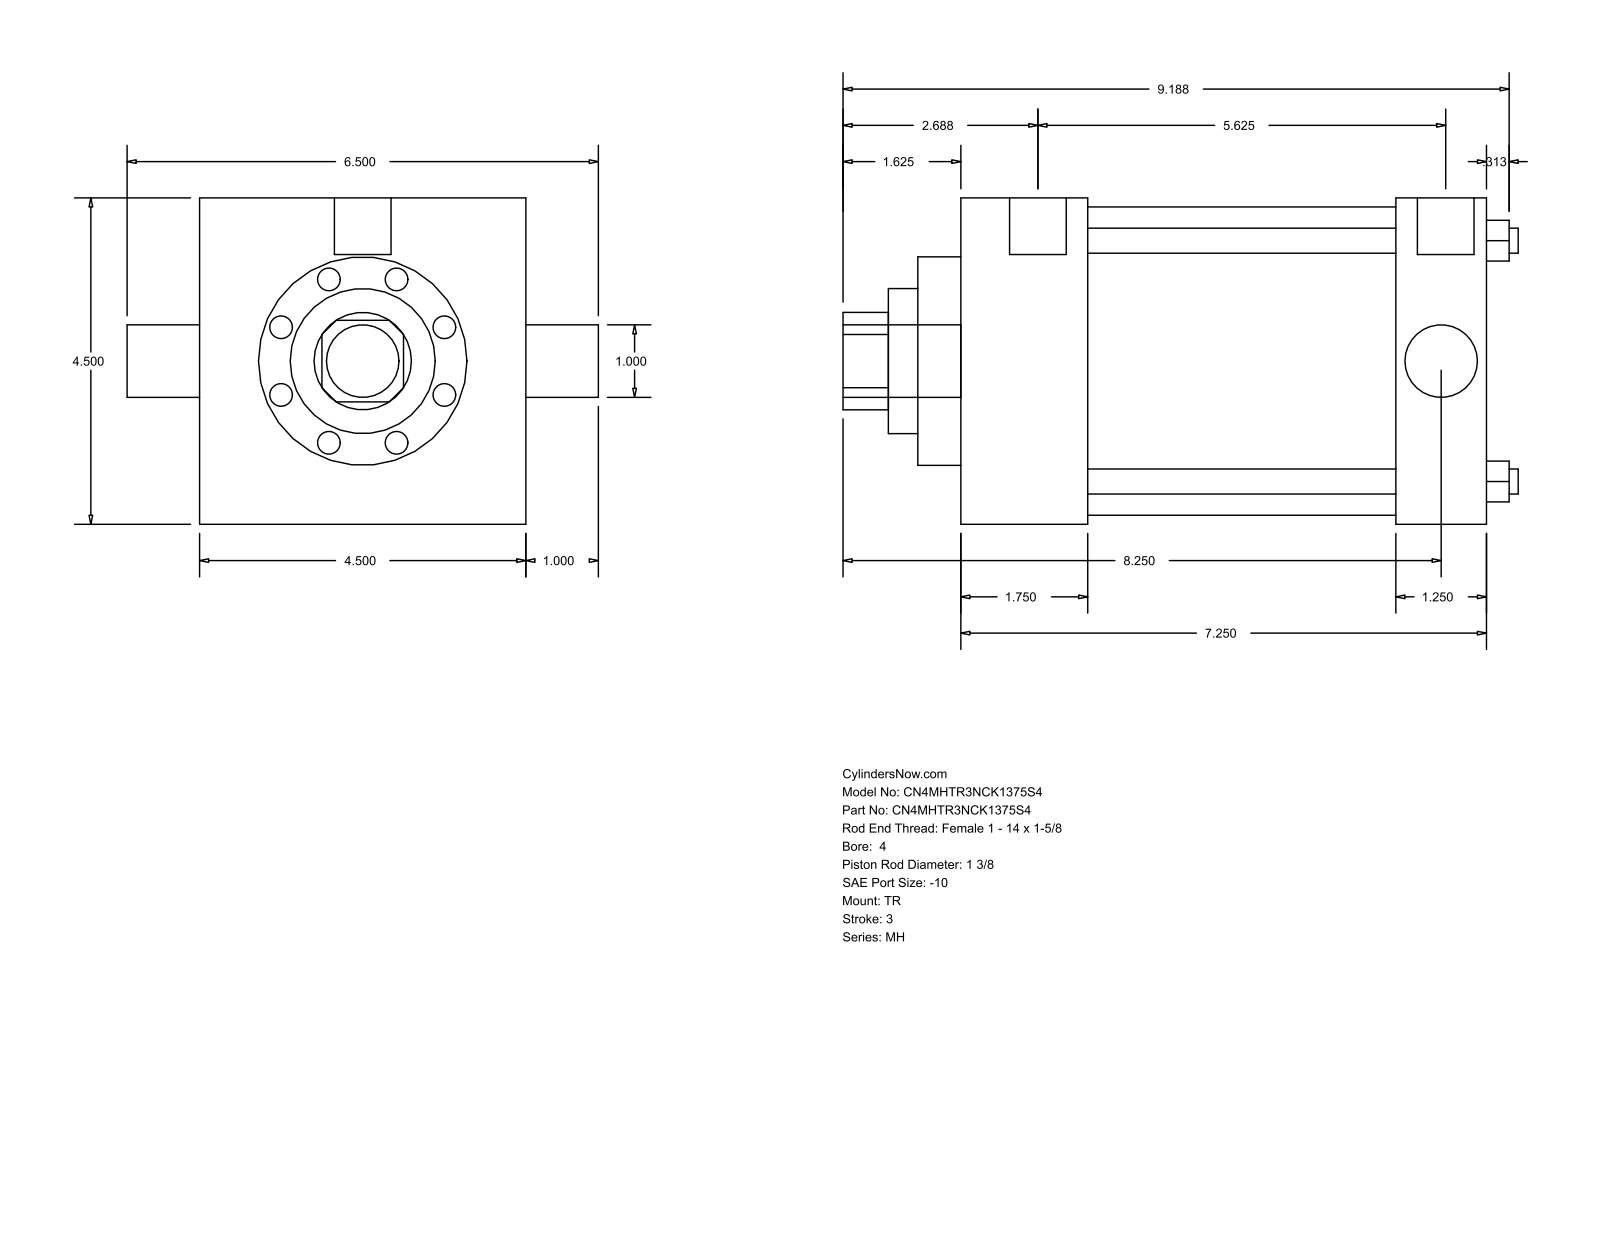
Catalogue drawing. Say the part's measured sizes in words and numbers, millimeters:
The part is named "MH_TR__0400_1.375". Its 3-D file was written by "GSSL Pune (CONFIG_CONTROL_DESIGN)". It is 0 solids with 86 faces: 61 planar, 25 cylindrical and 0 other. Overall it measures 236.54 by 165.1 by 114.3 millimeters. Round holes: 4 of diameter 8.76, 1 of diameter 25.4, 1 of diameter 34.92, 1 of diameter 50.8, 1 of diameter 73.03, 1 of diameter 107.95. Round bosses or shafts: 3 of diameter 8.73, 2 of diameter 19.84, 1 of diameter 25.4. Partial cylindrical surfaces (rounded edges, fillets, slot ends): 1 of radius 17.06. The main face-to-face distances are 114.3, 184.16, 44.45, 139.71, 152.41, 107.96, 31.75, 15.08, 59.53, 167.49. The hole center spacings are 59.62, 84.32, 119.25.
